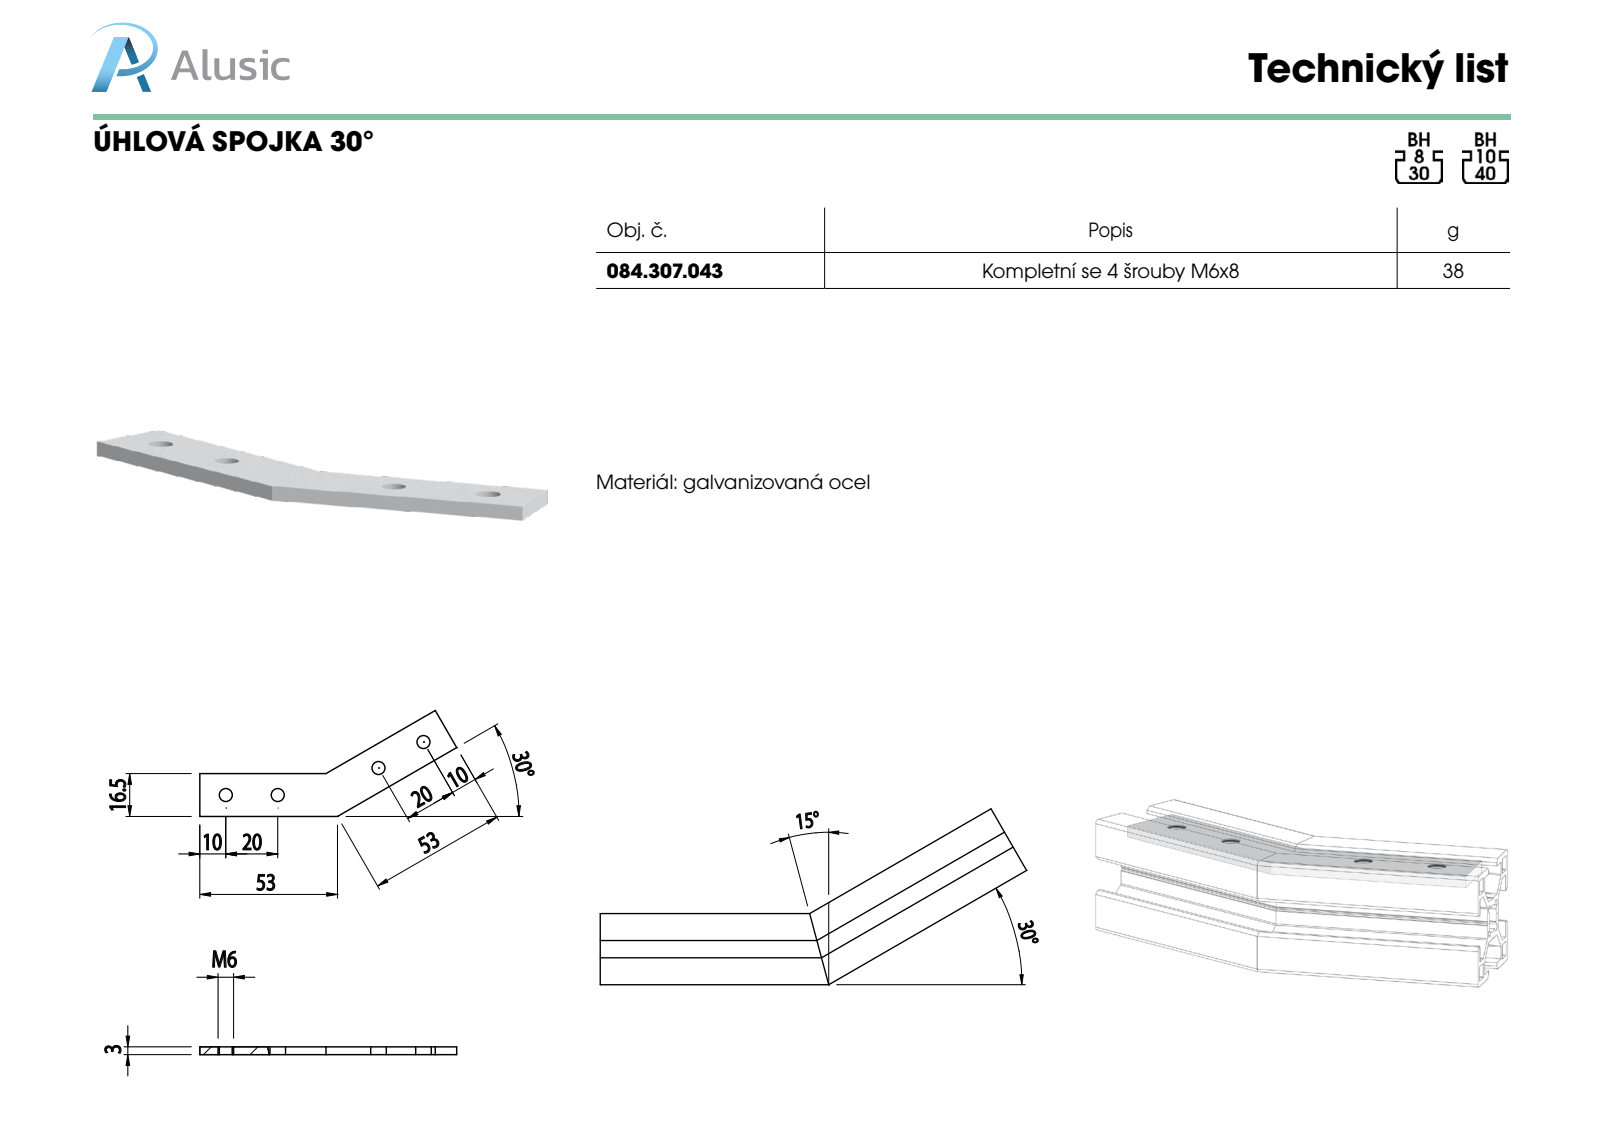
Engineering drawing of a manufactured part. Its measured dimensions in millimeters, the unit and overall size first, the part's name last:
Units: millimetres
Overall size (bounding box): 98.9 × 40.79 × 3
Round holes (diameter × count): ⌀5 ×4
Main face-to-face distances: 3, 16.5
Hole centre spacings: 20, 59.7, 40.16, 78.79
Volume: 4 793 mm³ · Surface area: 4 092 mm²
Bodies: 1 solid, 16 faces (8 planar, 8 cylindrical, 0 other)
Part name (STEP PRODUCT): 084.307.043
STEP written by: SolidWorks 2012 (CONFIG_CONTROL_DESIGN)
